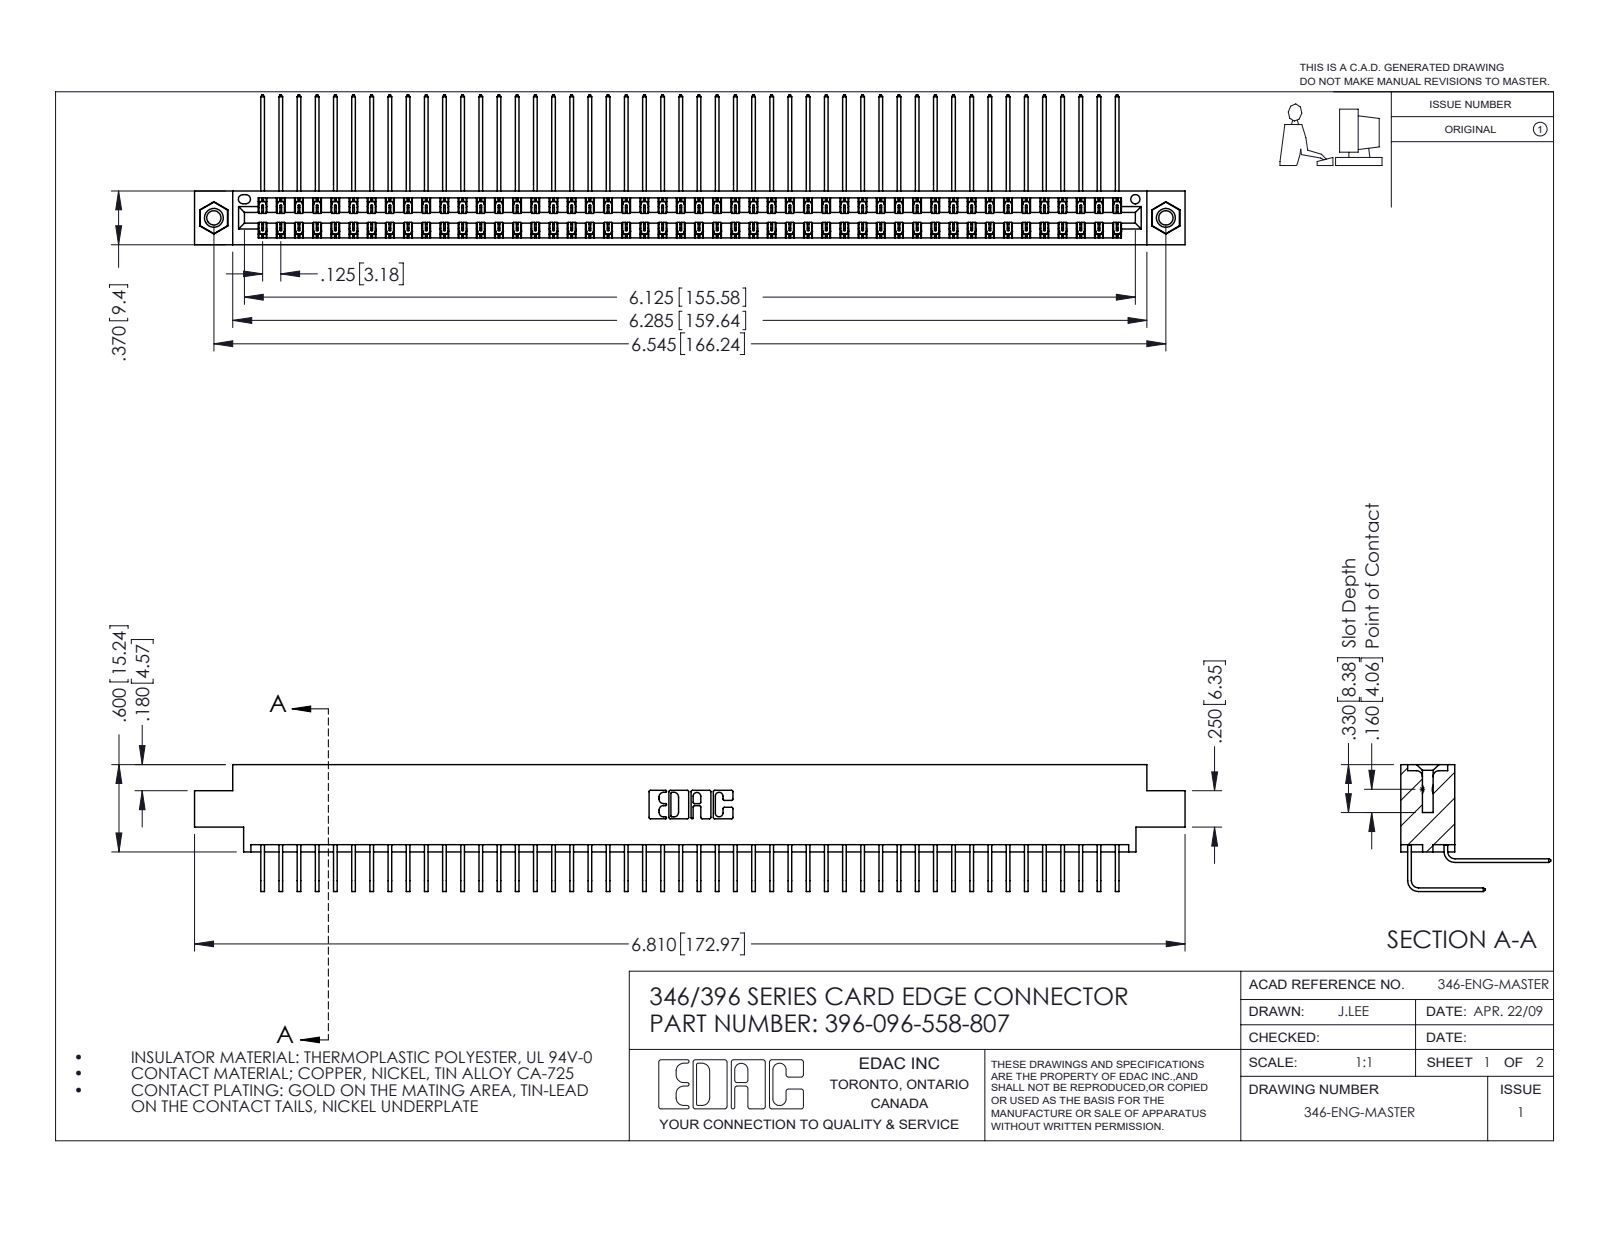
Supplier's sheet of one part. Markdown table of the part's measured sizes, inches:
| quantity | value |
| --- | --- |
| part name | 346 Part_0.170 Offset - 0.156 Dia-TI; 396-096-558-807; 345-250-001_345-250-005-103; 345-292-001_558 Tail - 2 (+1 more) |
| STEP written by | SolidWorks 2016 (CONFIG_CONTROL_DESIGN) |
| units | inches |
| bodies | 99 solids, 5370 faces (3664 planar, 1690 cylindrical, 16 other) |
| overall size | 6.81 × 1.03 × 0.873 |
| volume | 1.056 in³ |
| surface area | 41.45 in² |
| round holes (diameter × count) | 0.098 × 2, 0.125 × 2, 0.156 × 2, 0.064 × 1 |
| round bosses / shafts (diameter × count) | 0.155 × 2 |
| partial cylindrical surfaces (radius × count) | 0.006 × 144, 0.01 × 22, 0.007 × 6, 0.031 × 6, 0.026 × 3, 0.014 × 2, 0.022 × 2, 0.024 × 2 |
| main face-to-face distances | 0.322, 0.048, 0.025, 0.37, 0.25, 0.298, 0.072, 0.275, 0.222, 0.148 |
| hole center spacings | 0.246, 6.336, 6.545 |
